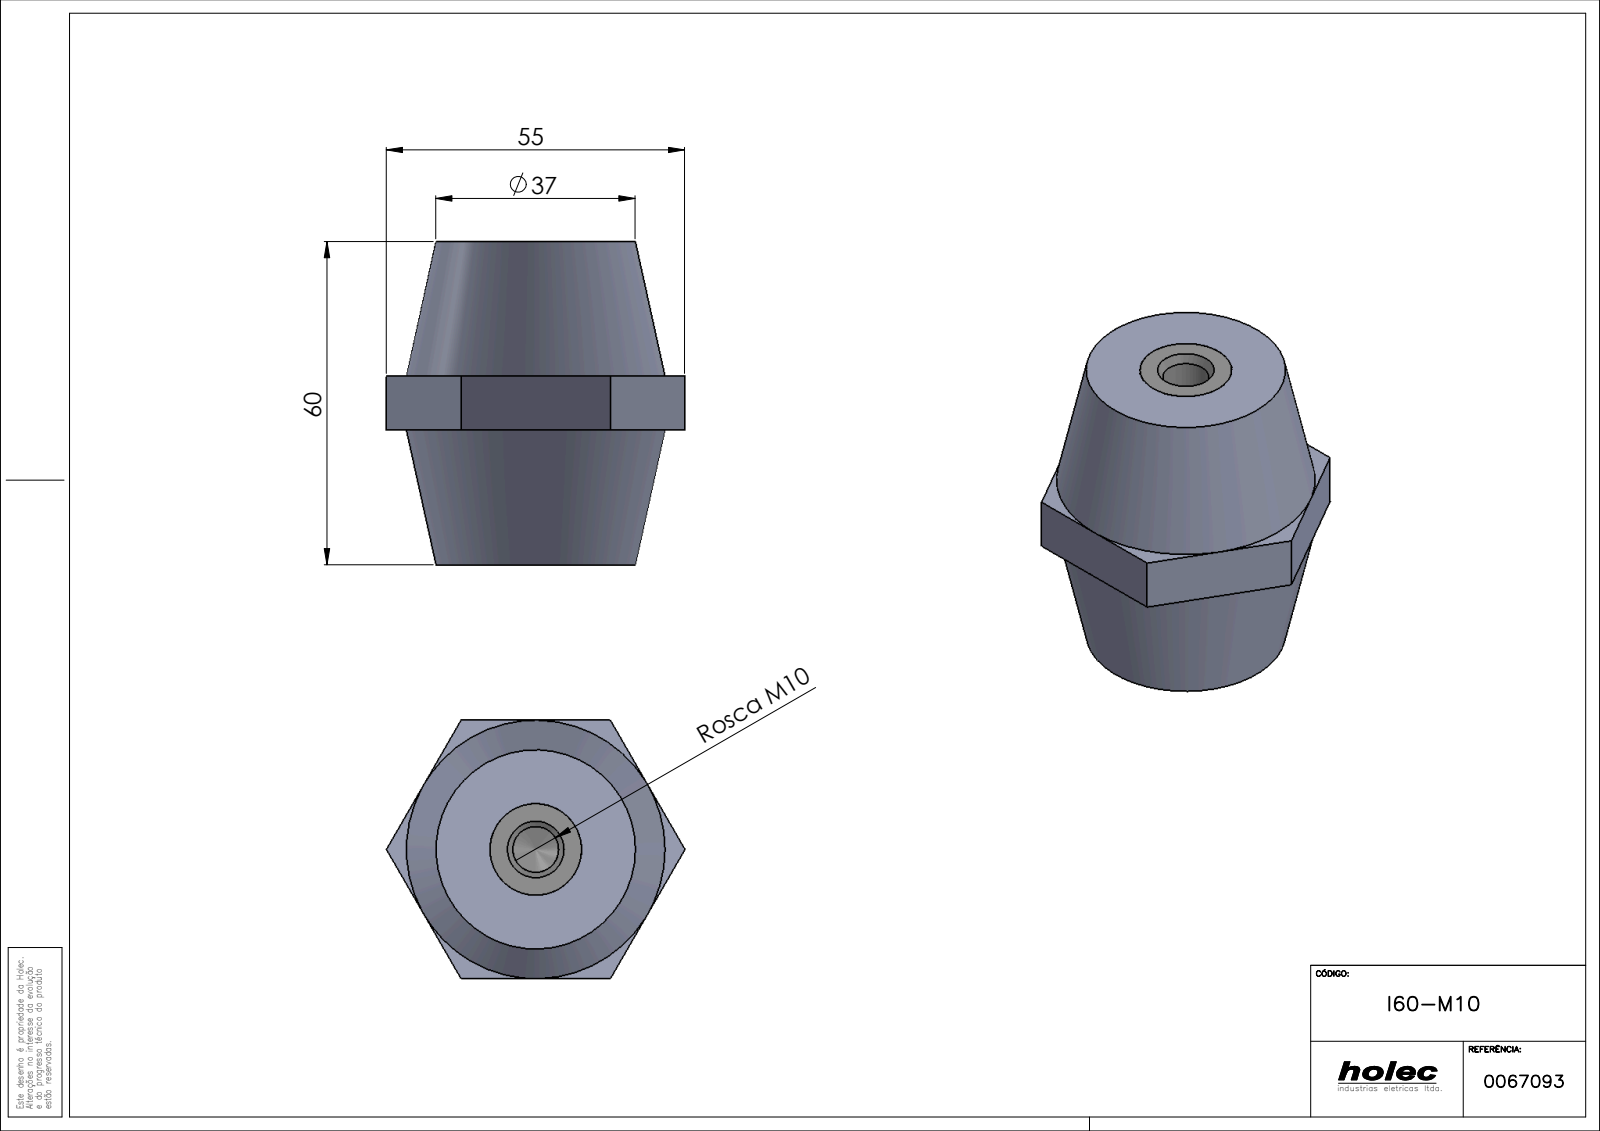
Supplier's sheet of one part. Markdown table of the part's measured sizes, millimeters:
| quantity | value |
| --- | --- |
| part name | PB1_0002; PB1_0108(PB1_0109_10); I60-M10 |
| STEP written by | SolidWorks 2017 (AUTOMOTIVE_DESIGN) |
| units | millimeters |
| bodies | 3 solids, 162 faces (82 planar, 12 cylindrical, 68 other) |
| overall size | 60 × 55.43 × 48 |
| volume | 89 560 mm³ |
| surface area | 17 066 mm² |
| round holes (diameter × count) | 8.5 × 1, 14 × 1 |
| main face-to-face distances | 17, 48, 60, 43.01, 43, 5, 12, 16.99, 26.01, 11.99 |
